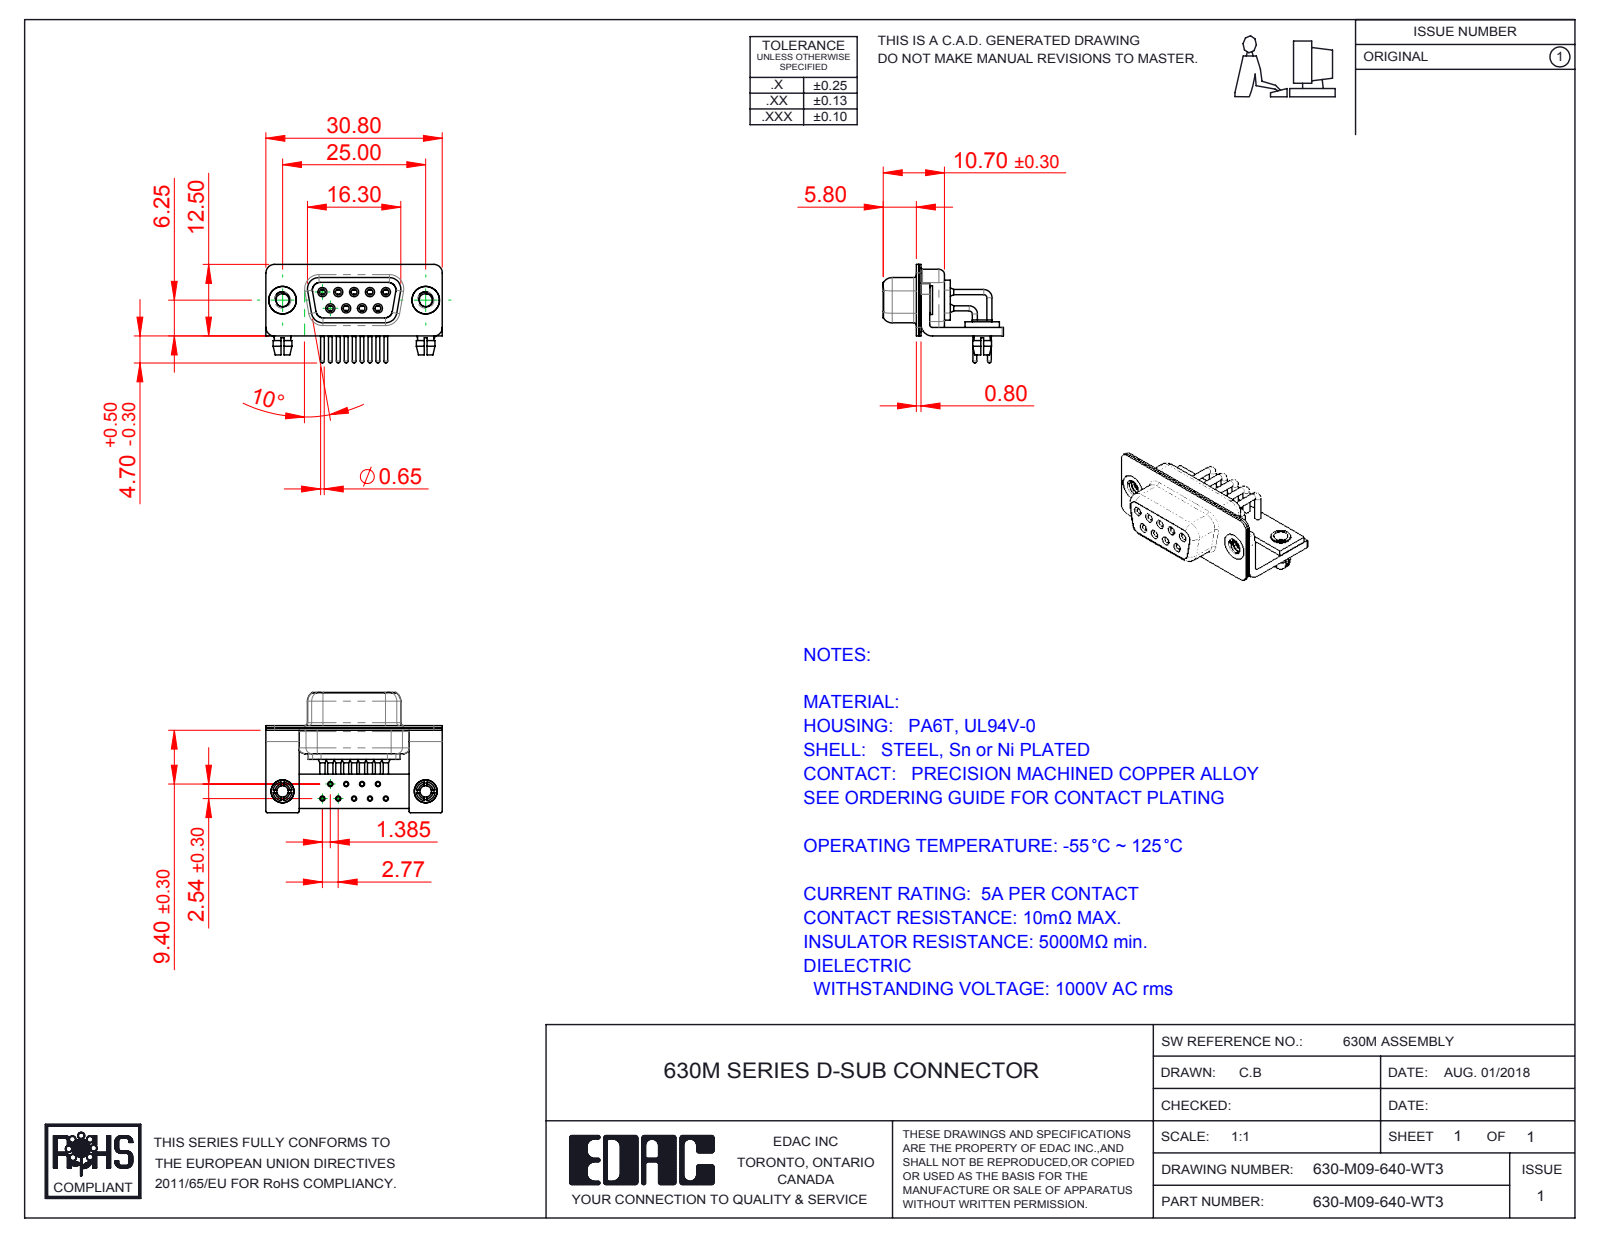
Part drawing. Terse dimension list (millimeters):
name: 630-M09-640-WT3; 630M Stabilizer Board_09 Contacts; 630M Contact Row 1; 630M Shell Rear_09 Contacts (+6 more)
written by: SolidWorks 2016 (CONFIG_CONTROL_DESIGN)
unit: mm
bodies: 19 solids, 916 faces (276 planar, 416 cylindrical, 224 other)
size: 30.8 × 21 × 17.2
volume: 2 237 mm³; area: 5 917 mm²
holes: 11× ⌀2, 9× ⌀0.9, 9× ⌀1, 9× ⌀1.1, 9× ⌀1.7, 9× ⌀1.8, 2× ⌀2.26, 2× ⌀2.5, 2× ⌀3.2, 2× ⌀4, 2× ⌀4.8
bosses: 9× ⌀1.6, 9× ⌀1.5, 9× ⌀0.9, 9× ⌀0.65, 2× ⌀5, 2× ⌀4.9, 2× ⌀4, 2× ⌀3.4
rounds: 16× R0.25, 16× R1.5, 13× R2, 8× R1.35, 8× R1.6, 5× R0.5, 4× R0.6, 4× R0.65
face distances: 0.4, 0.8, 1.5, 2.3, 1.9, 1, 9.35, 1.45, 2.5, 8.95
hole spacings: 2.77, 5.54, 3.16, 4.87, 8.31, 2.89, 2.9, 5.03
